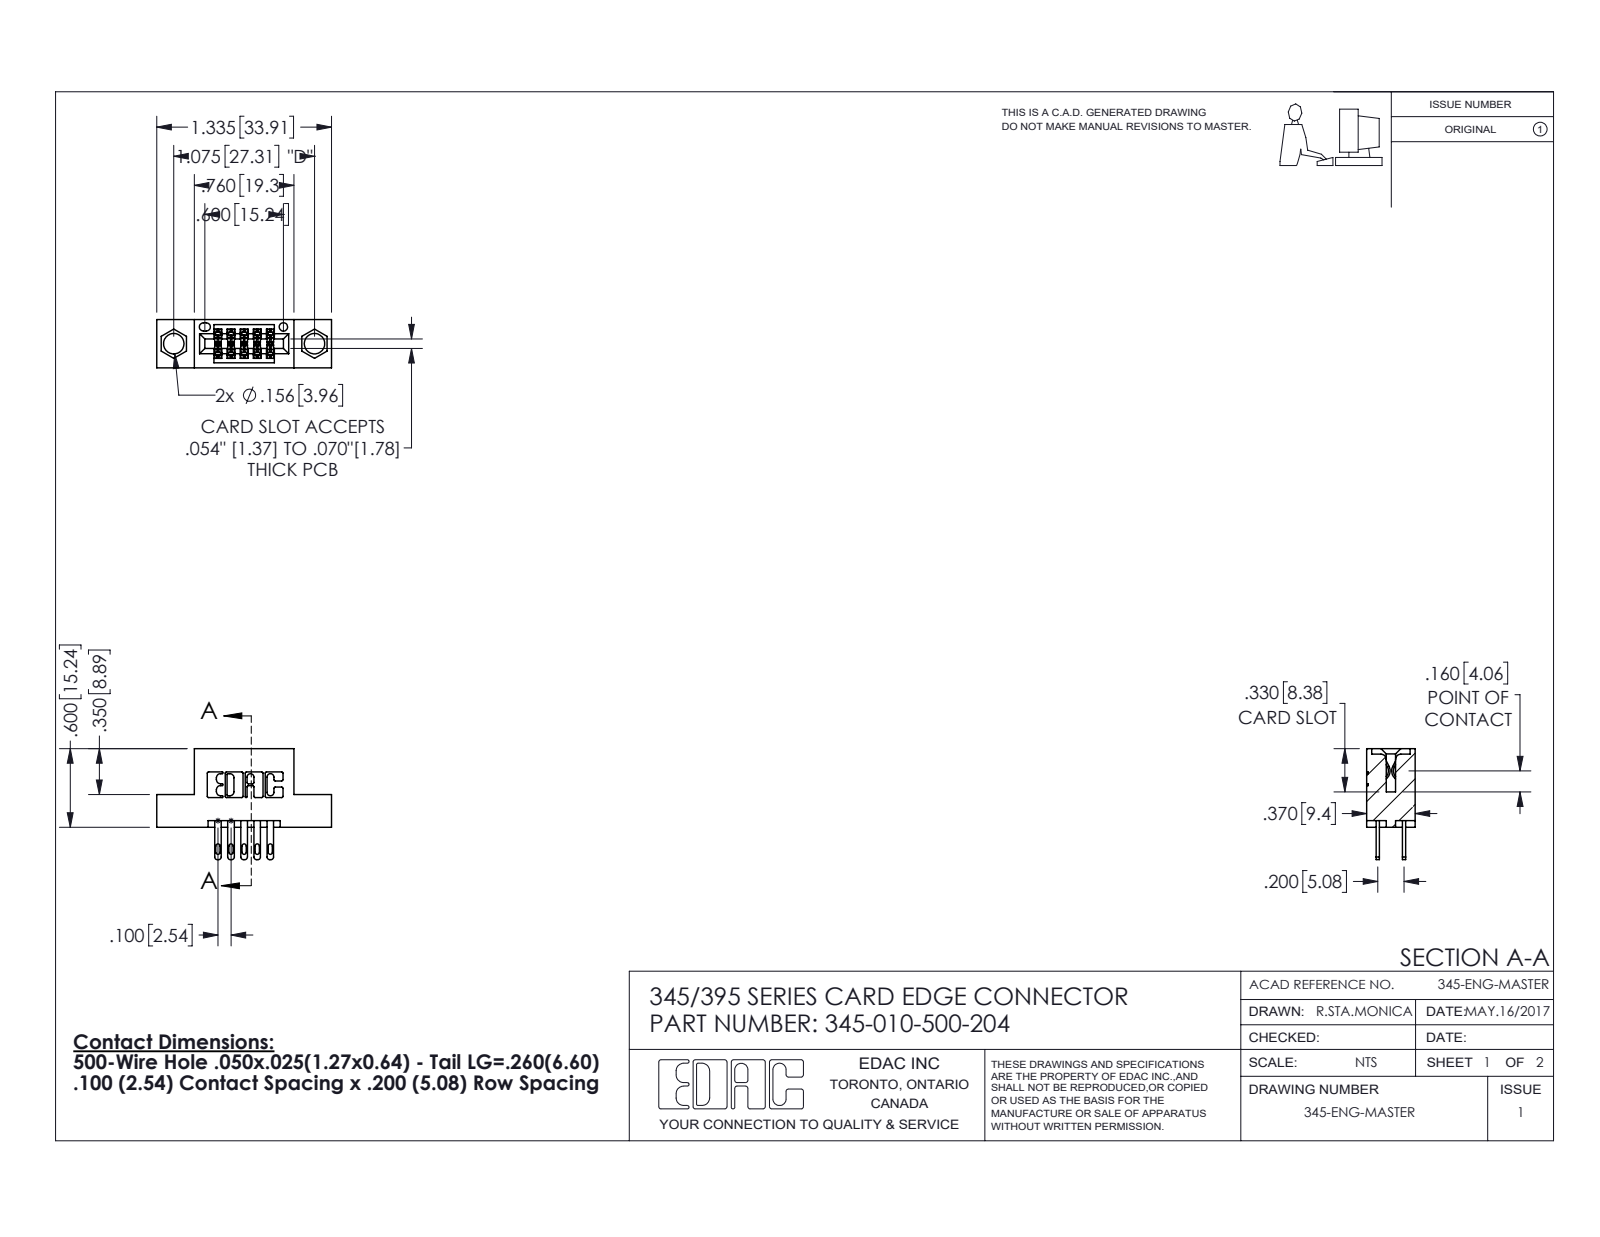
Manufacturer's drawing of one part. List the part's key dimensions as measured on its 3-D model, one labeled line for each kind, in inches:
Part name (STEP PRODUCT): 345-010-500-204; 345 Part_Flush Mounting Lugs - 0.156 Dia-TI; 345-292-001_345-293-100
STEP written by: SolidWorks 2020 (CONFIG_CONTROL_DESIGN)
Units: inches
Bodies: 11 solids, 600 faces (364 planar, 236 cylindrical, 0 other)
Overall size (bounding box): 1.335 × 0.847 × 0.37
Volume: 0.175 in³ · Surface area: 5.405 in²
Round holes (diameter × count): ⌀0.156 ×2, ⌀0.064 ×1
Partial cylindrical surfaces — rounded edges, fillets, slot ends (radius × count): R0.01 ×22, R0.006 ×15, R0.016 ×10, R0.02 ×10, R0.007 ×6, R0.031 ×6, R0.026 ×3, R0.014 ×2
Main face-to-face distances: 0.2, 0.298, 0.072, 0.37, 0.1, 0.098, 0.272, 0.025, 0.25, 0.225
Hole centre spacings: 0.27, 0.847, 1.075
